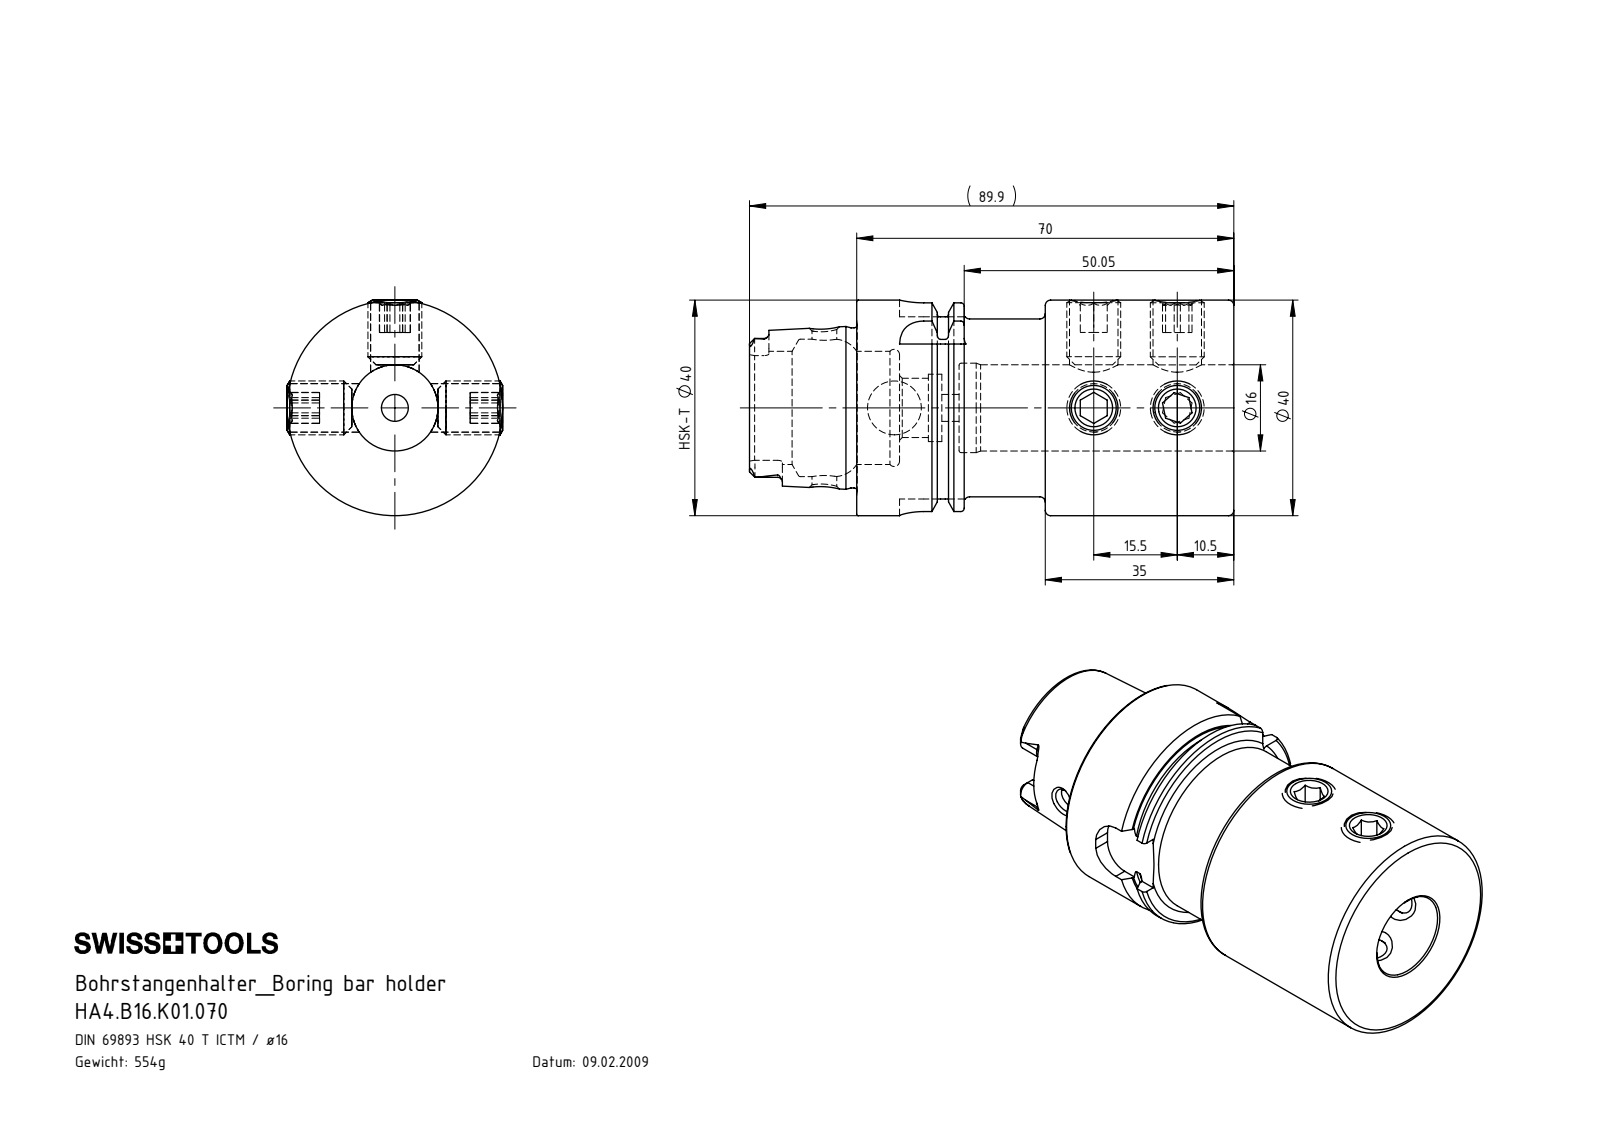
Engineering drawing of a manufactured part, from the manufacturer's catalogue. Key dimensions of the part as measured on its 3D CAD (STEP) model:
Part name (STEP PRODUCT): HA4-B16.K01.070_B_Fertigbearbeitung; HA4.B16.K01.070; ISO 4026 - M10 x 12_PreviewCfg
STEP written by: SolidWorks 2017 (AUTOMOTIVE_DESIGN)
Units: millimetres
Bodies: 7 solids, 287 faces (102 planar, 76 cylindrical, 109 other)
Overall size (bounding box): 89.9 × 40 × 40
Volume: 70 561 mm³ · Surface area: 23 530 mm²
Round holes (diameter × count): ⌀9 ×4, ⌀4.6 ×1, ⌀5 ×1, ⌀10 ×1, ⌀11 ×1, ⌀12.5 ×1, ⌀16 ×1, ⌀16.6 ×1, ⌀21 ×1, ⌀25.5 ×1
Round bosses / shafts (diameter × count): ⌀10 ×4, ⌀40 ×1, ⌀34.75 ×1, ⌀33 ×1, ⌀29.71 ×1
Partial cylindrical surfaces — rounded edges, fillets, slot ends (radius × count): R0.9 ×6, R1.88 ×4, R4.5 ×4
Main face-to-face distances: 70, 35, 12, 5, 6, 16, 7.95, 62.05, 19, 11.05
Hole centre spacings: 15.5, 37, 50, 52.5, 65.5
